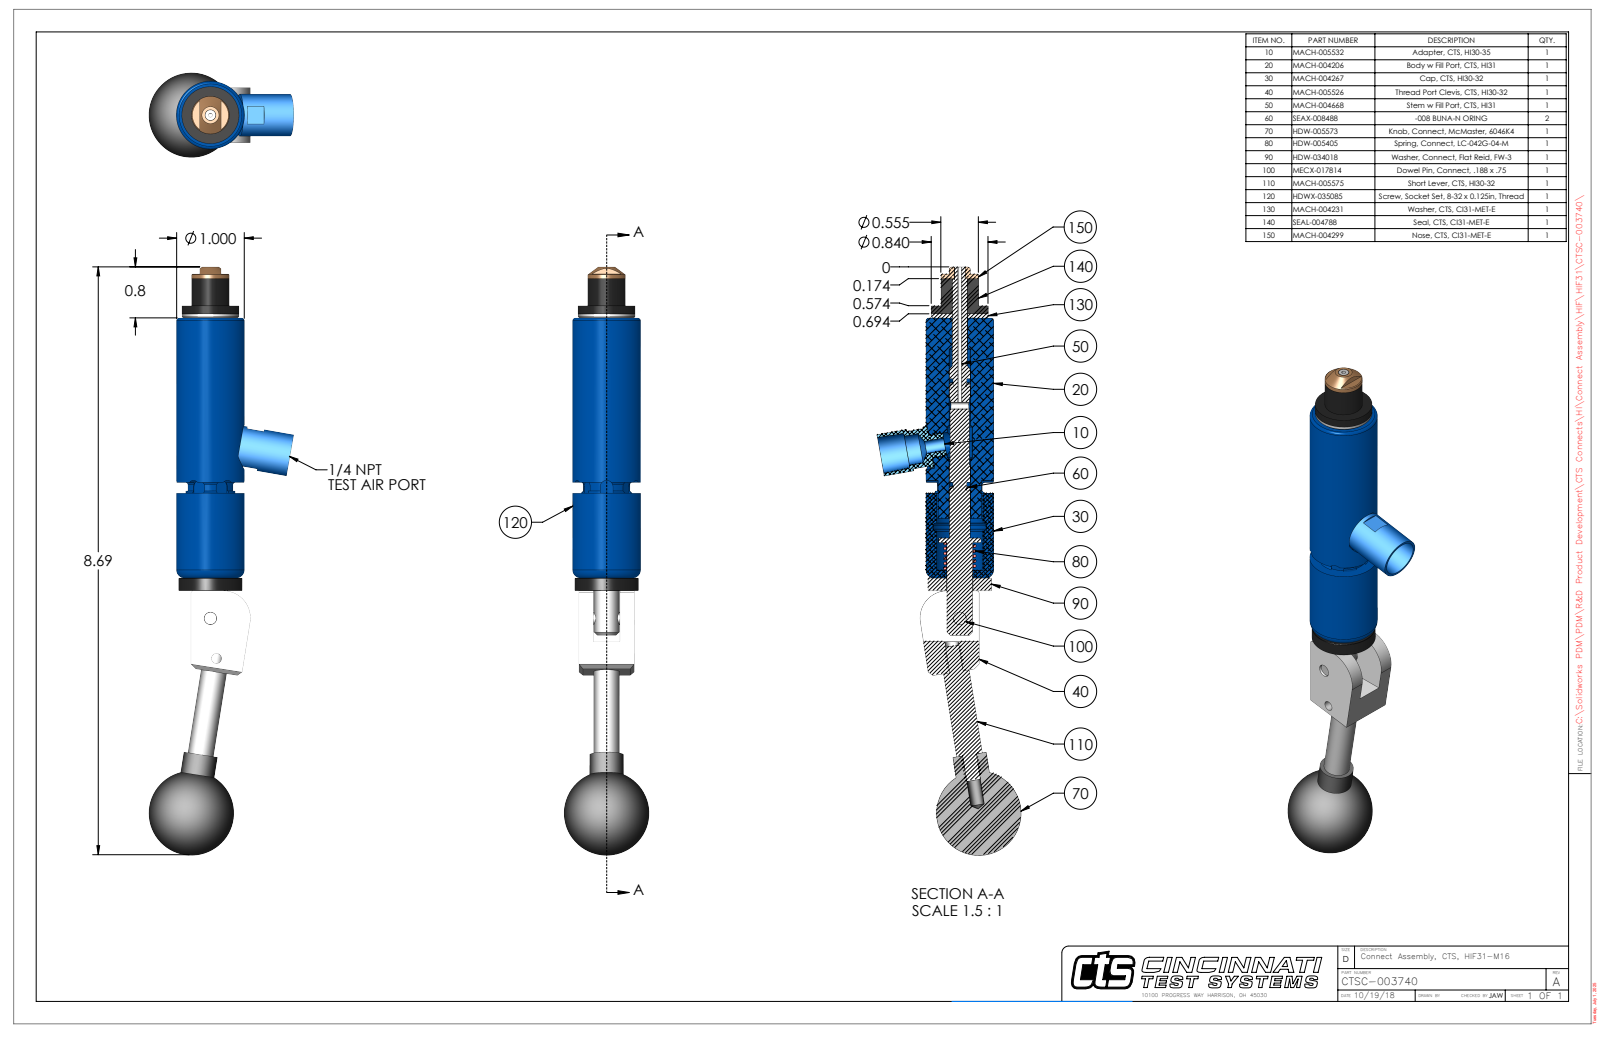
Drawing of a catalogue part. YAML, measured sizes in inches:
part_name: "CTSC-003740"
step_written_by: "SolidWorks 2023 (AUTOMOTIVE_DESIGN)"
units: inches
bodies: {solids: 9, faces: 303, planar: 113, cylindrical: 125, other: 65}
overall_size: [8.692, 2.128, 1.25]
volume: 5.174
surface_area: 40.35
round_holes:
  - {diameter: 0.201, count: 2}
  - {diameter: 0.063, count: 1}
  - {diameter: 0.109, count: 1}
  - {diameter: 0.136, count: 1}
  - {diameter: 0.15, count: 1}
  - {diameter: 0.159, count: 1}
  - {diameter: 0.187, count: 1}
  - {diameter: 0.189, count: 1}
  - {diameter: 0.218, count: 1}
  - {diameter: 0.228, count: 1}
  - {diameter: 0.229, count: 1}
  - {diameter: 0.385, count: 1}
round_bosses_or_shafts:
  - {diameter: 1, count: 1}
  - {diameter: 0.936, count: 1}
  - {diameter: 0.84, count: 1}
  - {diameter: 0.837, count: 1}
  - {diameter: 0.62, count: 1}
  - {diameter: 0.555, count: 1}
  - {diameter: 0.555, count: 1}
  - {diameter: 0.5, count: 1}
partial_cylinders:
  - {radius: 0.093, count: 6}
  - {radius: 0.029, count: 2}
  - {radius: 0.063, count: 1}
  - {radius: 0.325, count: 1}
  - {radius: 0.375, count: 1}
  - {radius: 0.4, count: 1}
  - {radius: 0.465, count: 1}
face_to_face_distances: [0.21, 0.602, 0.06, 3.9, 3.841, 0.812, 4.088, 4.028, 0.187, 0.391]
hole_center_spacings: [0.599, 1.658, 2.252]
